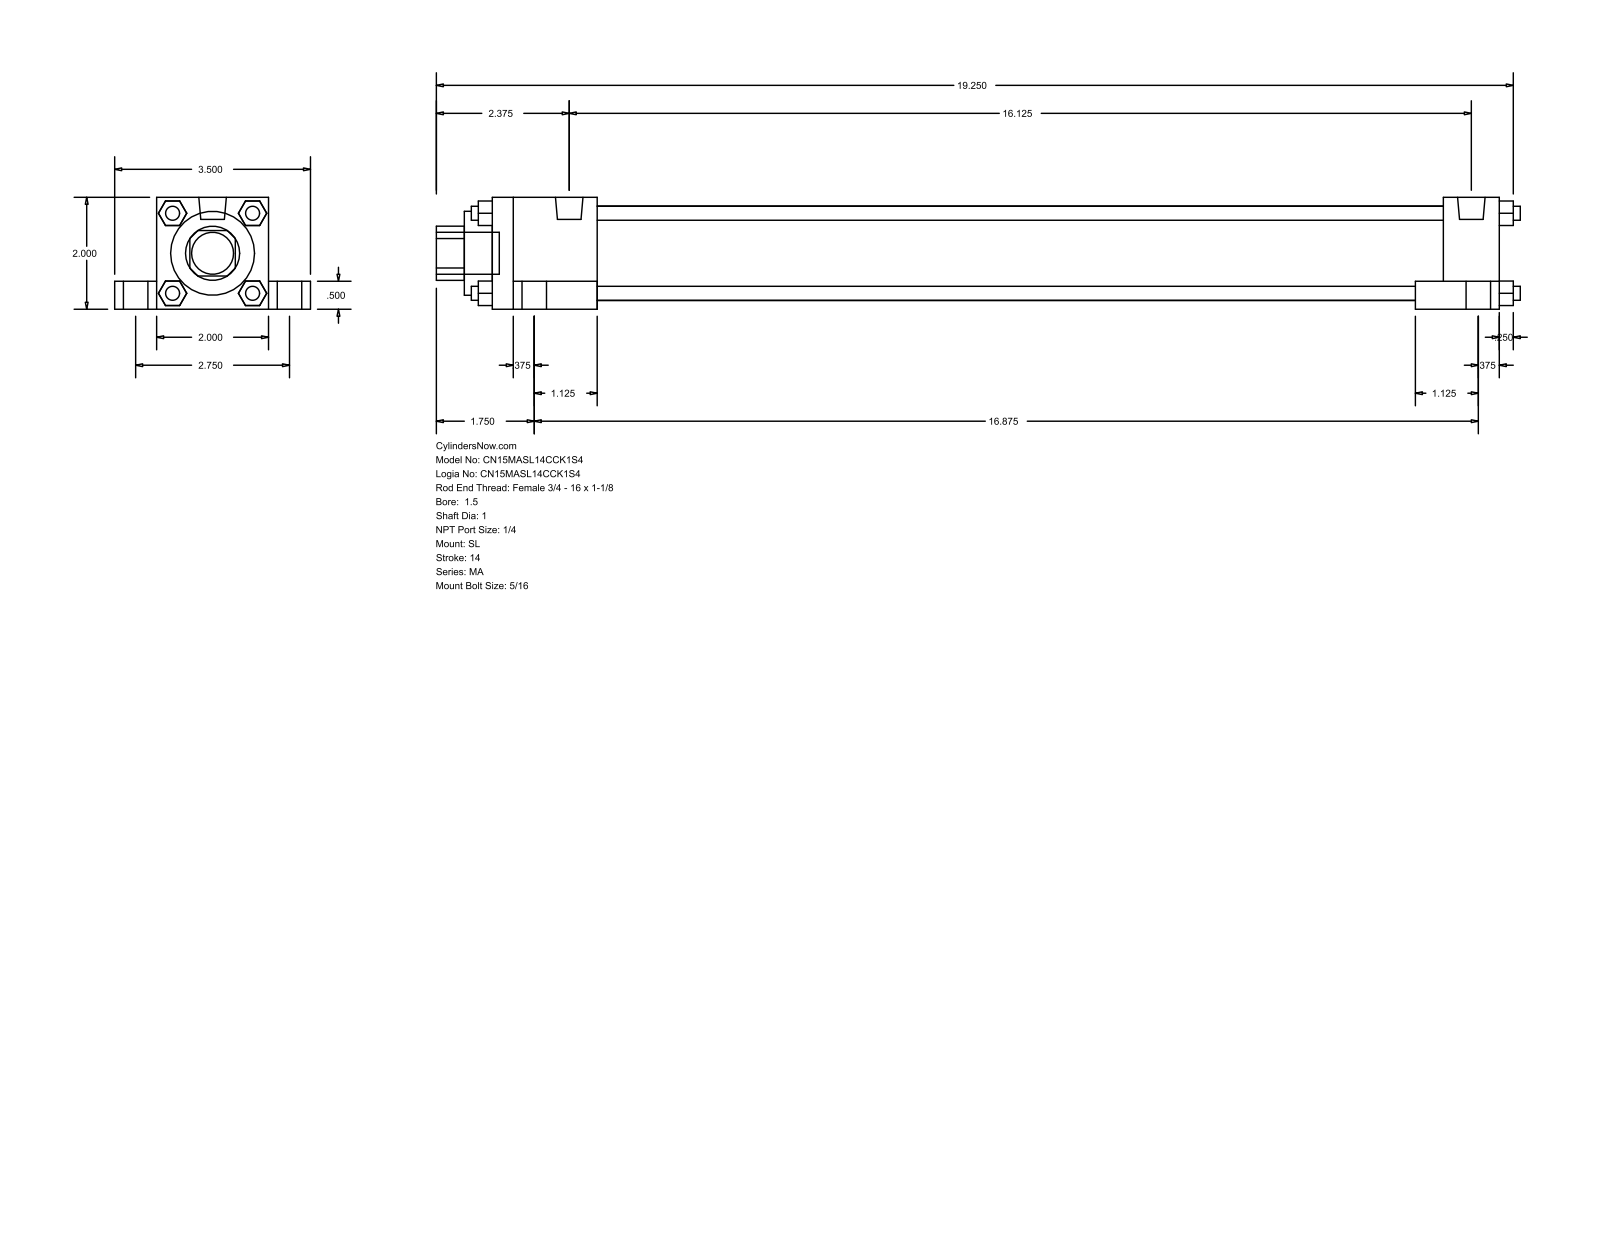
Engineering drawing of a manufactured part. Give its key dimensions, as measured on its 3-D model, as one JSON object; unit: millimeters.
{"part_name": "MA_SL__0150_1", "step_written_by": "GSSL Pune (CONFIG_CONTROL_DESIGN)", "units": "millimeters", "bodies": {"solids": 0, "faces": 148, "planar": 112, "cylindrical": 36, "other": 0}, "overall_size": [492.12, 88.9, 50.8], "round_holes": [[25.4, 1], [38.1, 1], [42.93, 1]], "round_bosses_or_shafts": [[17.46, 4], [11.11, 4], [7.94, 4], [6.35, 4], [12.49, 2], [19.05, 1]], "partial_cylinders_radius": [[12.29, 1]], "face_to_face_distances": [50.8, 12.7, 19.05, 9.52, 69.85, 38.1, 6.35, 457.2, 25.4, 431.8]}
